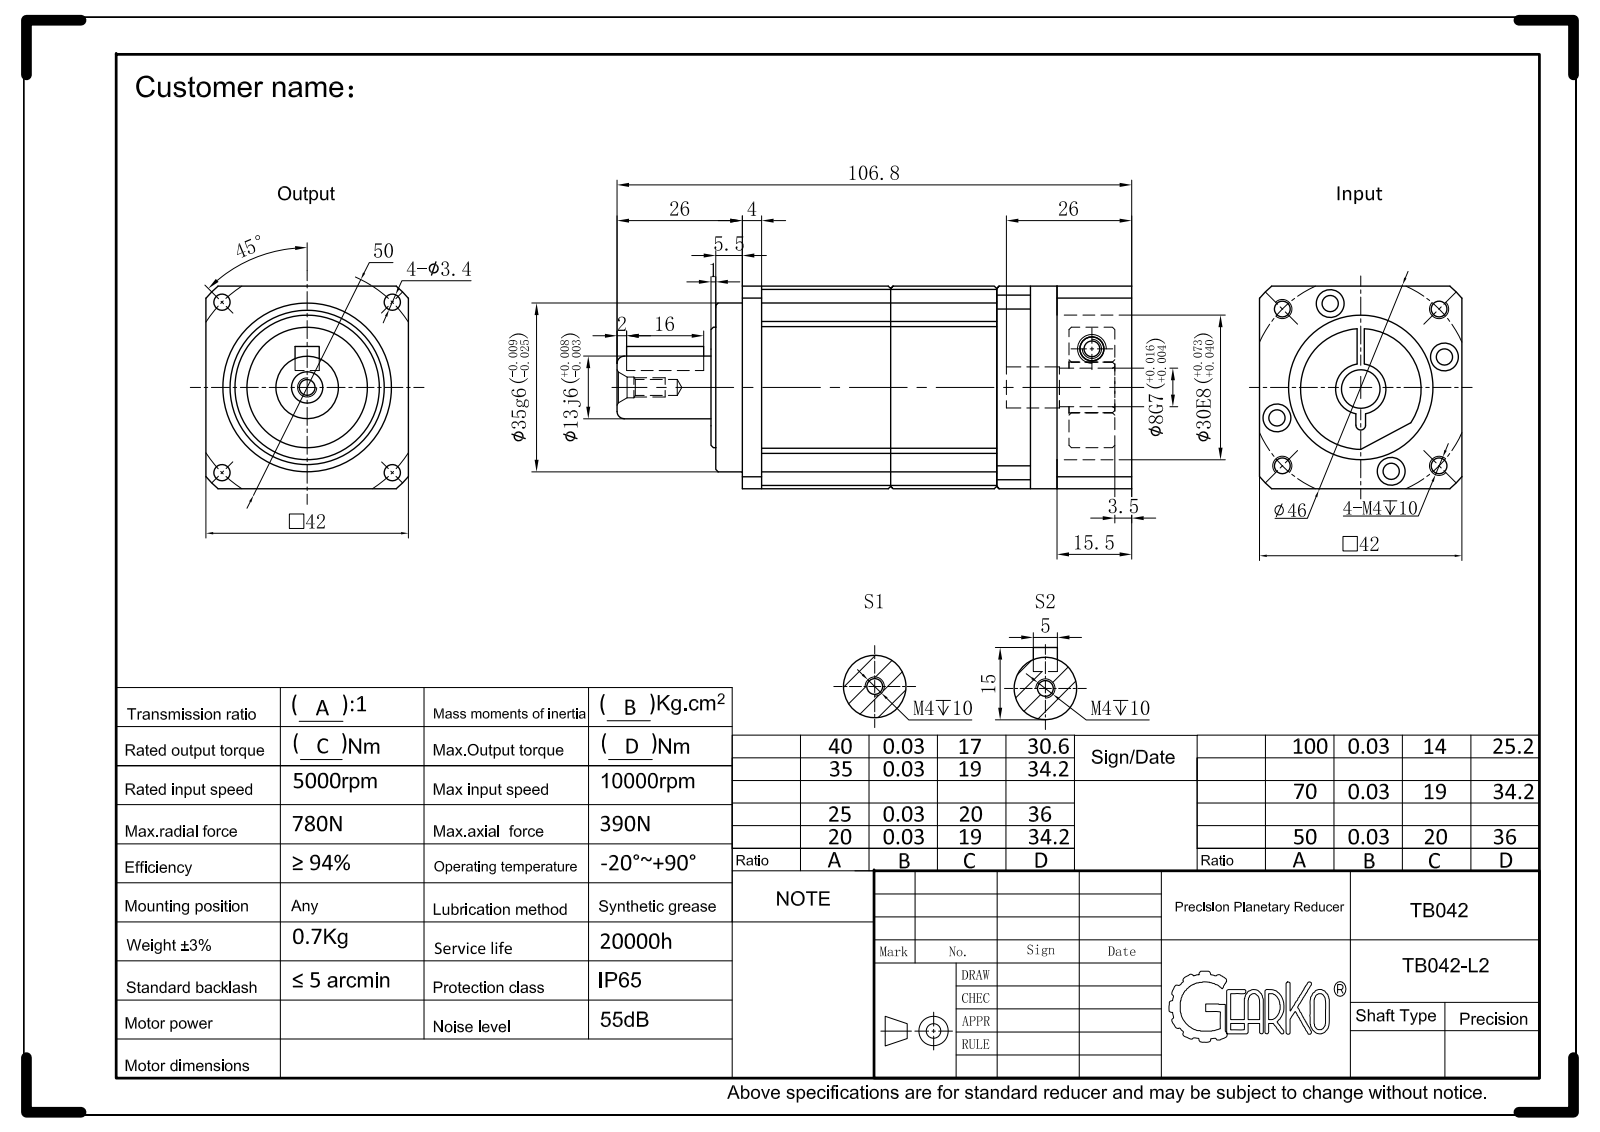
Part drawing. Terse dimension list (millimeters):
name: TB042-L2-8-30-46-M4-26-4; JJT-001; CQB-001; 042-fla-46-m4 (+4 more)
written by: SolidWorks 2017 (CONFIG_CONTROL_DESIGN)
unit: mm
bodies: 7 solids, 325 faces (124 planar, 157 cylindrical, 44 other)
size: 106.8 × 42 × 42
volume: 134 751 mm³; area: 36 379 mm²
holes: 8× ⌀3.4, 5× ⌀6, 4× ⌀3.2, 1× ⌀1.6, 1× ⌀3.3, 1× ⌀4, 1× ⌀4.3, 1× ⌀4.5, 1× ⌀7.7, 1× ⌀8, 1× ⌀8.5, 1× ⌀10.5
bosses: 1× ⌀42, 1× ⌀37, 1× ⌀35, 1× ⌀25.03, 1× ⌀17, 1× ⌀16, 1× ⌀15, 1× ⌀14.5
rounds: 8× R0.5, 4× R3, 4× R4, 2× R2.5, 1× R1, 1× R24.5, 1× R28
face distances: 42, 22, 3, 12.5, 34.5, 15.5, 58.3, 25, 5.5, 37.5
hole spacings: 33.97, 2, 11.35, 22.62, 23, 25, 48, 26.16
